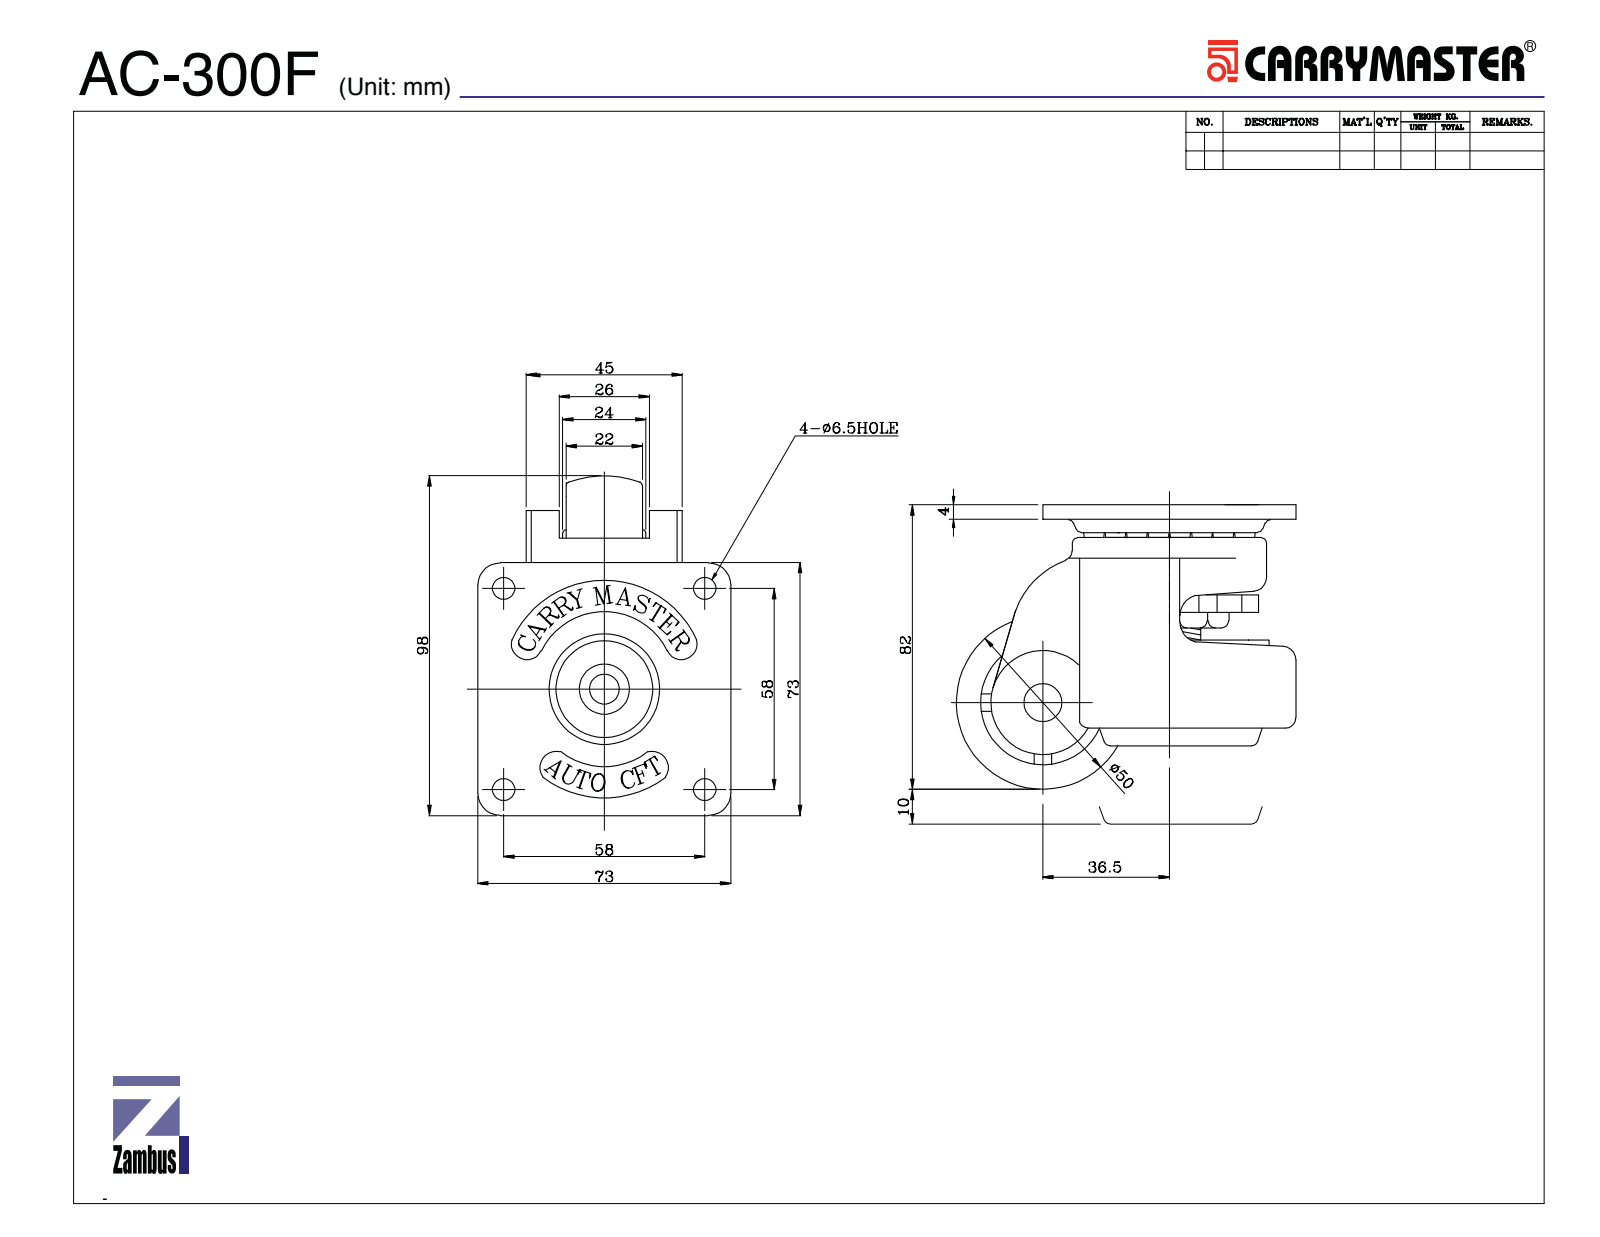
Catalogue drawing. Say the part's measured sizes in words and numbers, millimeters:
The part is named "AC-300F FOOT MOUNT(RUBBER); AC-300F HANDLE ASSY; AC-300F FOOT MOUNT ASSY; AC-300F FOOT MOUNT (+8 more)". Its 3-D file was written by "SolidWorks 2016 (CONFIG_CONTROL_DESIGN)". It is 47 solids with 1446 faces: 497 planar, 310 cylindrical and 639 other. Overall it measures 100.5 by 82 by 73 millimeters. Its volume is 206 132 cubic millimeters and its surface area 91 284 square millimeters. Round holes: 4 of diameter 6.5, 1 of diameter 2.5, 1 of diameter 6.8, 1 of diameter 8.5, 1 of diameter 10.2, 1 of diameter 12.5, 1 of diameter 17.5, 1 of diameter 18, 1 of diameter 28, 1 of diameter 36, 1 of diameter 40. Round bosses or shafts: 2 of diameter 19, 2 of diameter 10, 2 of diameter 8, 1 of diameter 58, 1 of diameter 41.2, 1 of diameter 38, 1 of diameter 25, 1 of diameter 20. Partial cylindrical surfaces (rounded edges, fillets, slot ends): 64 of radius 1, 16 of radius 2, 13 of radius 3, 9 of radius 5, 6 of radius 2.5, 4 of radius 0.5, 4 of radius 1.5, 4 of radius 6.5. The main face-to-face distances are 10, 20, 3.5, 23.5, 31.04, 4, 50.54, 54.54, 15, 5. The hole center spacings are 41.01, 58, 82.02.
